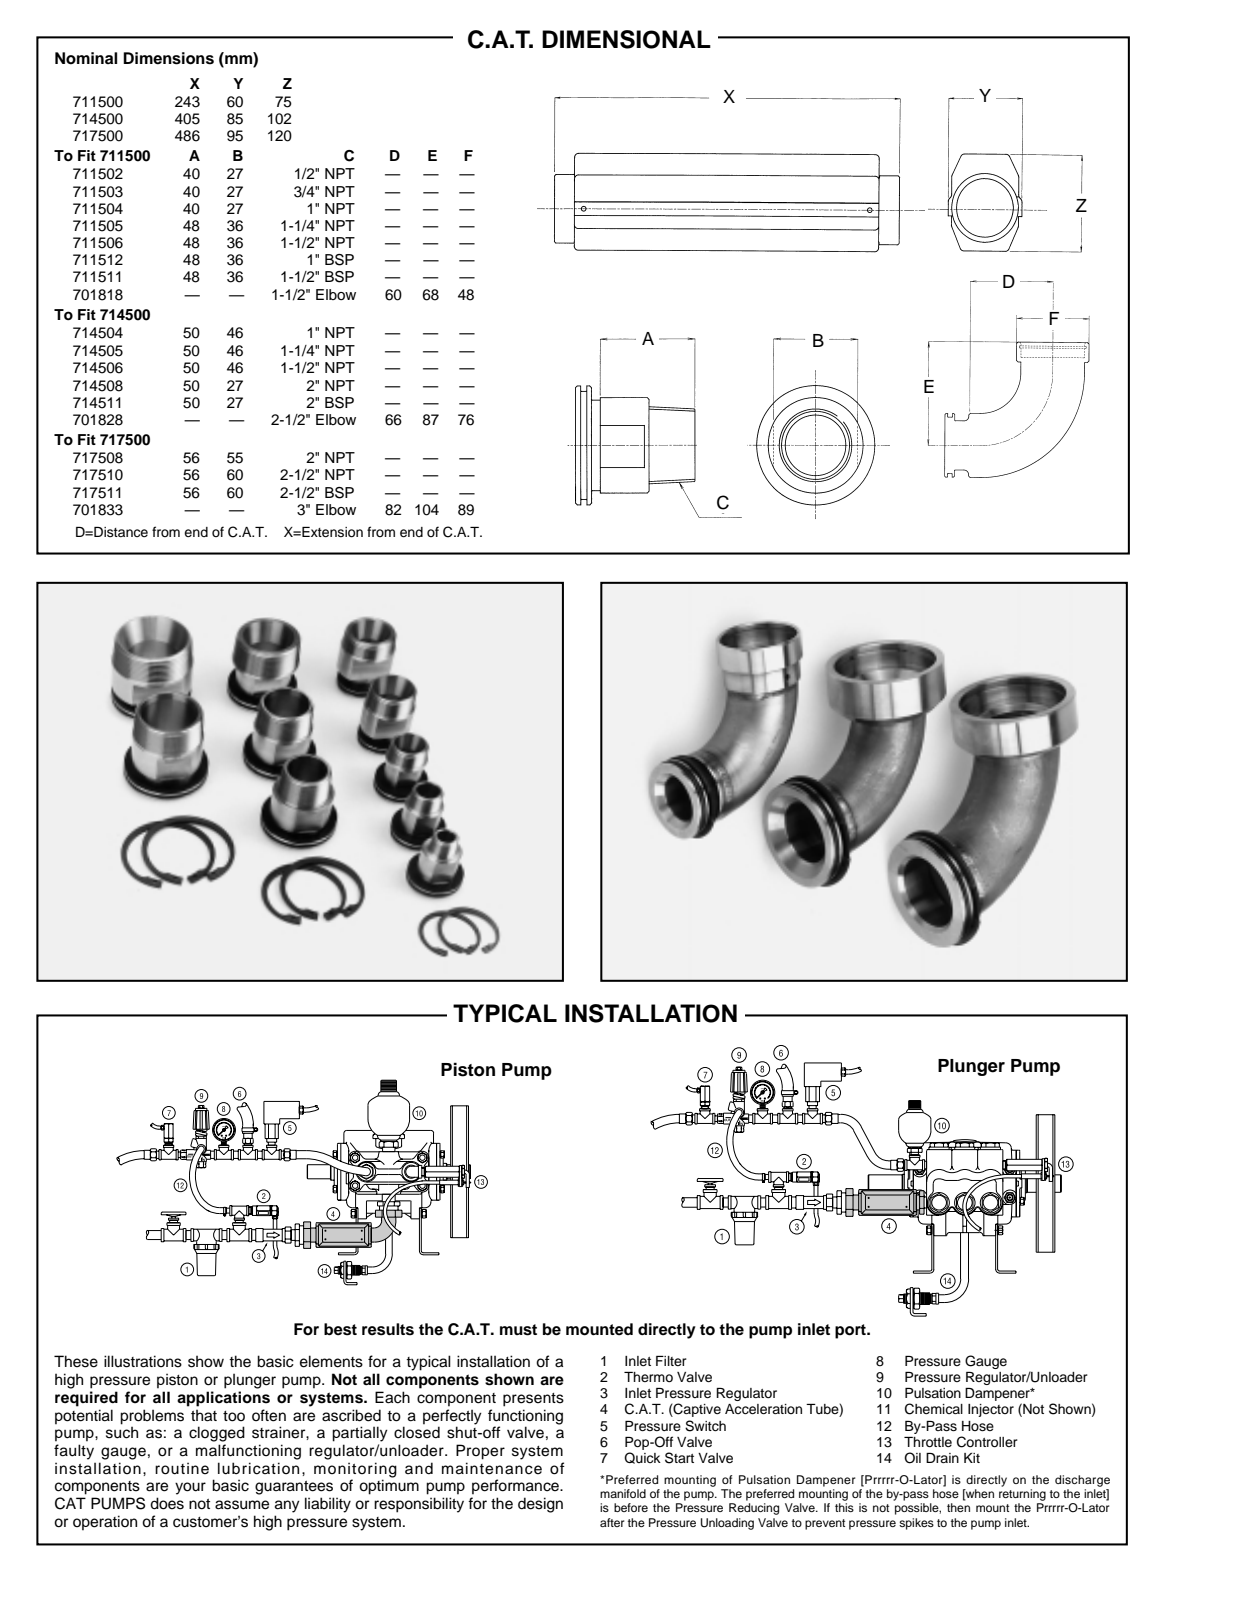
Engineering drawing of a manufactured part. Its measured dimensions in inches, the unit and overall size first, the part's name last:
Units: inches
Overall size (bounding box): 9.725 × 2.838 × 2.15
Round holes (diameter × count): ⌀1.212 ×1, ⌀1.774 ×1
Round bosses / shafts (diameter × count): ⌀1.994 ×1
Partial cylindrical surfaces — rounded edges, fillets, slot ends (radius × count): R0.03 ×32, R0.1 ×8
Main face-to-face distances: 2.37, 2.838, 0.065, 2.085, 2.02, 2.15, 0.16, 8.535, 8.375, 8.695
Volume: 35.96 in³ · Surface area: 128.8 in²
Bodies: 1 solid, 112 faces (22 planar, 58 cylindrical, 32 other)
Part name (STEP PRODUCT): 711500
STEP written by: SolidWorks 2011 (CONFIG_CONTROL_DESIGN)
